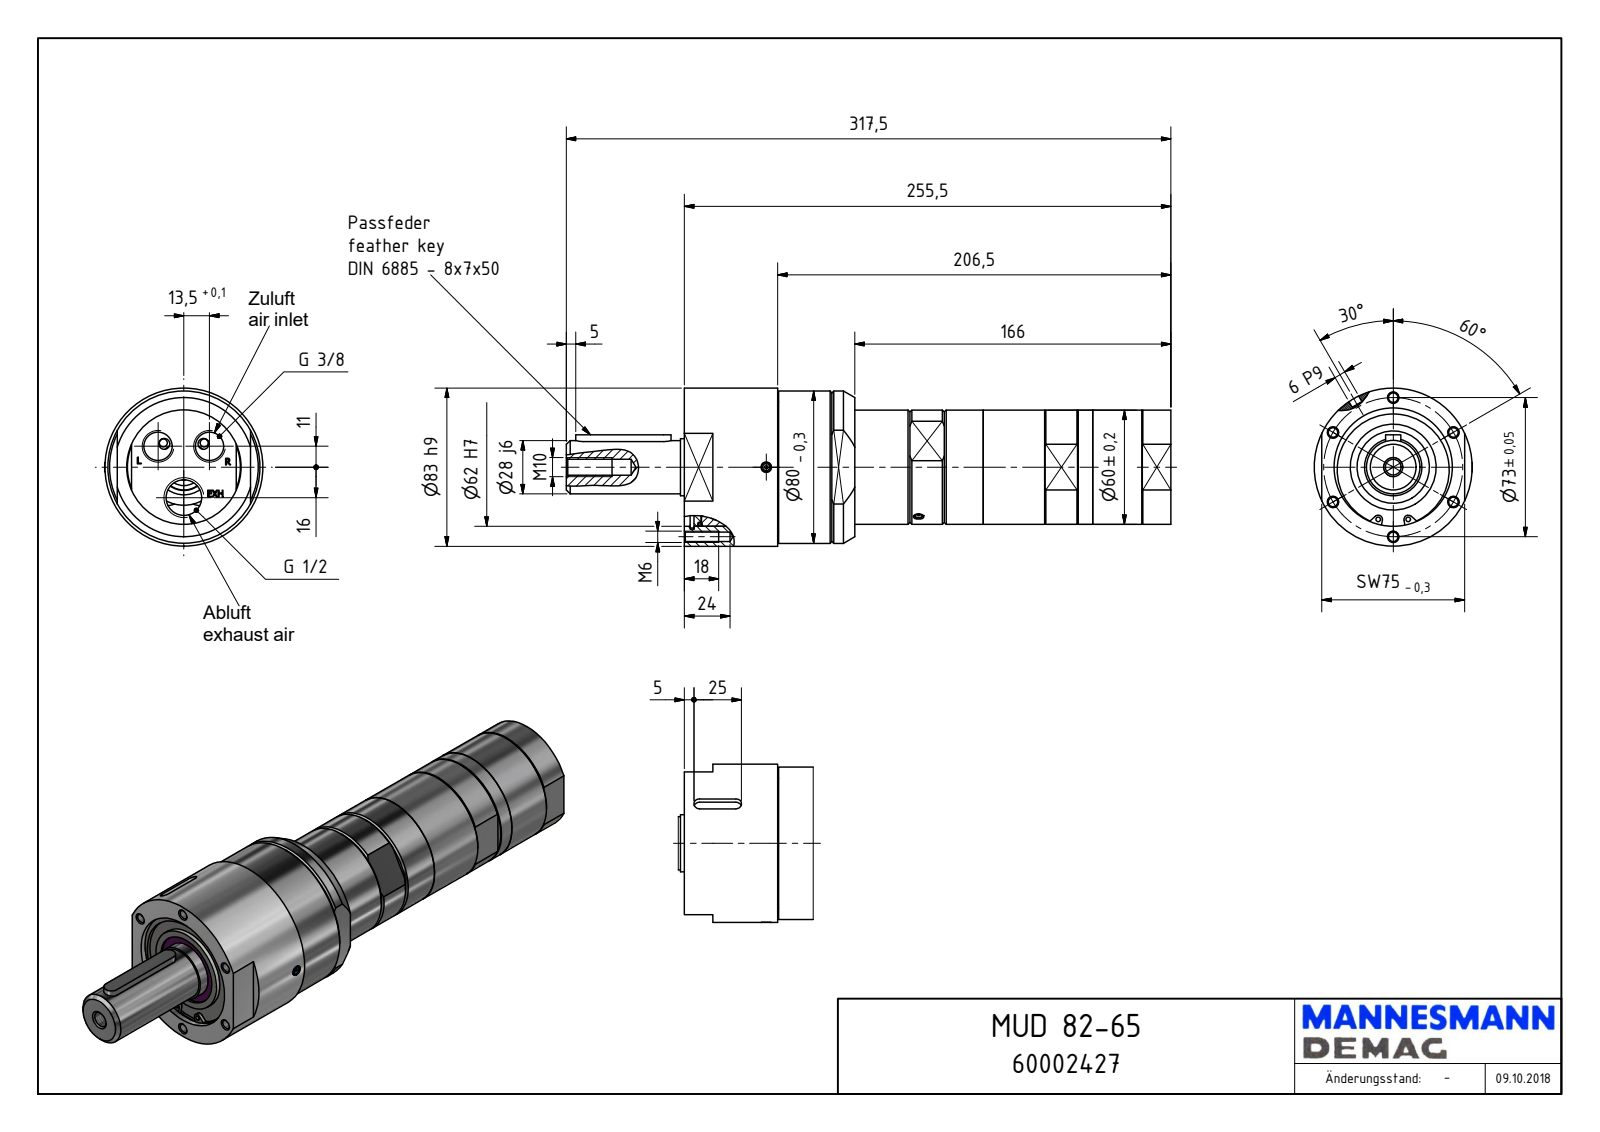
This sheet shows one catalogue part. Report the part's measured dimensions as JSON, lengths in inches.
{"part_name": "MUD 82-65_60002427", "step_written_by": "Autodesk Inventor 2018 (AUTOMOTIVE_DESIGN)", "units": "inches", "bodies": {"solids": 1, "faces": 572, "planar": 221, "cylindrical": 280, "other": 71}, "overall_size": [12.5, 3.268, 3.268], "volume_in3": 57.16, "surface_area_in2": 136.1, "round_holes": [[0.194, 6], [0.061, 2], [0.098, 2], [0.157, 2], [0.217, 2], [0.589, 2], [0.33, 1], [0.733, 1], [1.496, 1], [1.575, 1], [2.311, 1], [2.441, 1]], "round_bosses_or_shafts": [[0.197, 2], [0.142, 2], [3.268, 1], [3.15, 1], [2.684, 1], [2.362, 1], [1.772, 1], [1.181, 1]], "partial_cylinders_radius": [[0.138, 94], [0.308, 7], [0.398, 3], [0.089, 2], [0.118, 2], [0.157, 2], [0.295, 2], [0.335, 1]], "face_to_face_distances": [10.059, 1.929, 8.13, 0.02, 2.559, 3.524, 1.594, 6.535, 0.098, 0.182], "hole_center_spacings": [1.437, 2.489, 2.874, 0.476, 0.544, 0.685, 0.725, 0.768]}
